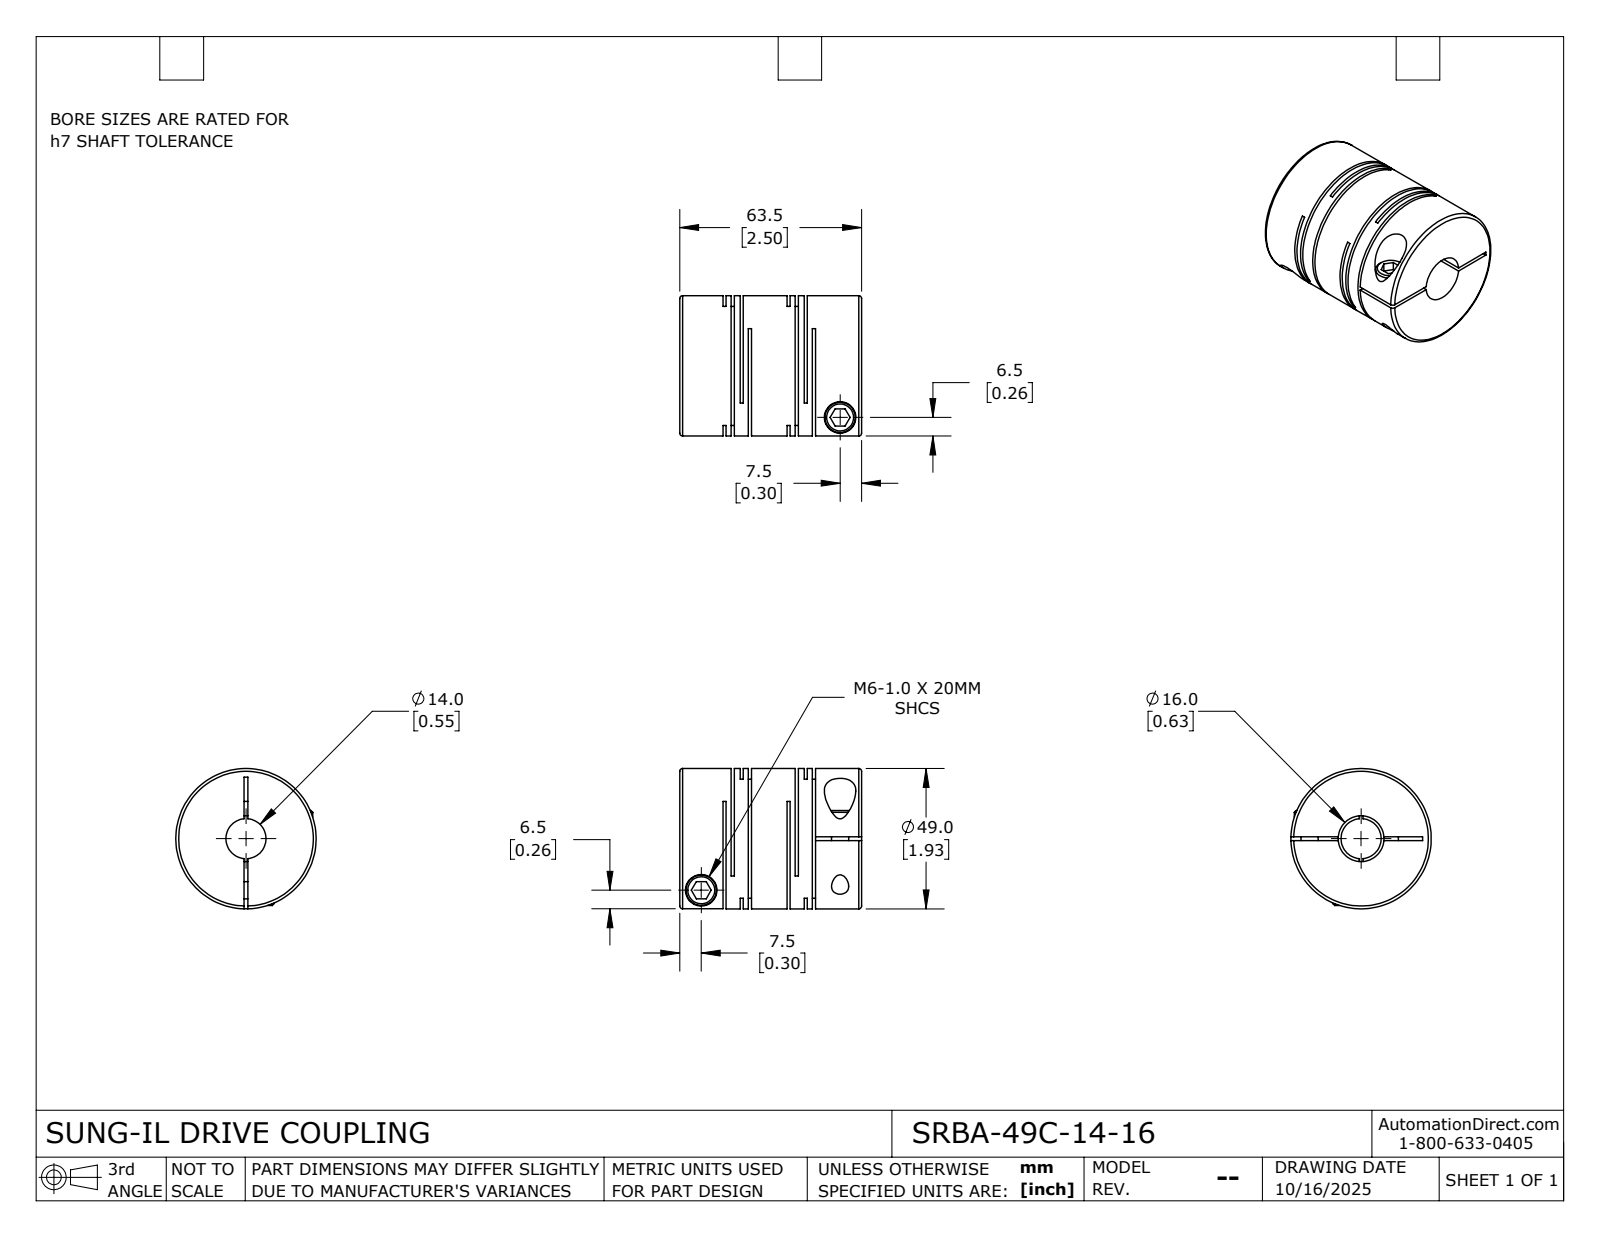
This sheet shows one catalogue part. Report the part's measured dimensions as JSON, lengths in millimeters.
{"part_name": "SRBA-49C-14-16", "step_written_by": "SolidWorks 2024 (CONFIG_CONTROL_DESIGN)", "units": "millimeters", "bodies": {"solids": 1, "faces": 115, "planar": 60, "cylindrical": 42, "other": 13}, "overall_size": [63.5, 49, 49], "volume_mm3": 92906, "surface_area_mm2": 39607, "round_holes": [[6, 2], [11, 2], [14, 1], [16, 1]], "round_bosses_or_shafts": [[10.6, 2], [49, 1]], "face_to_face_distances": [6, 1.1, 22.35, 2.85, 21.25, 3.15, 1.75, 4.9, 19.5, 16.35]}
